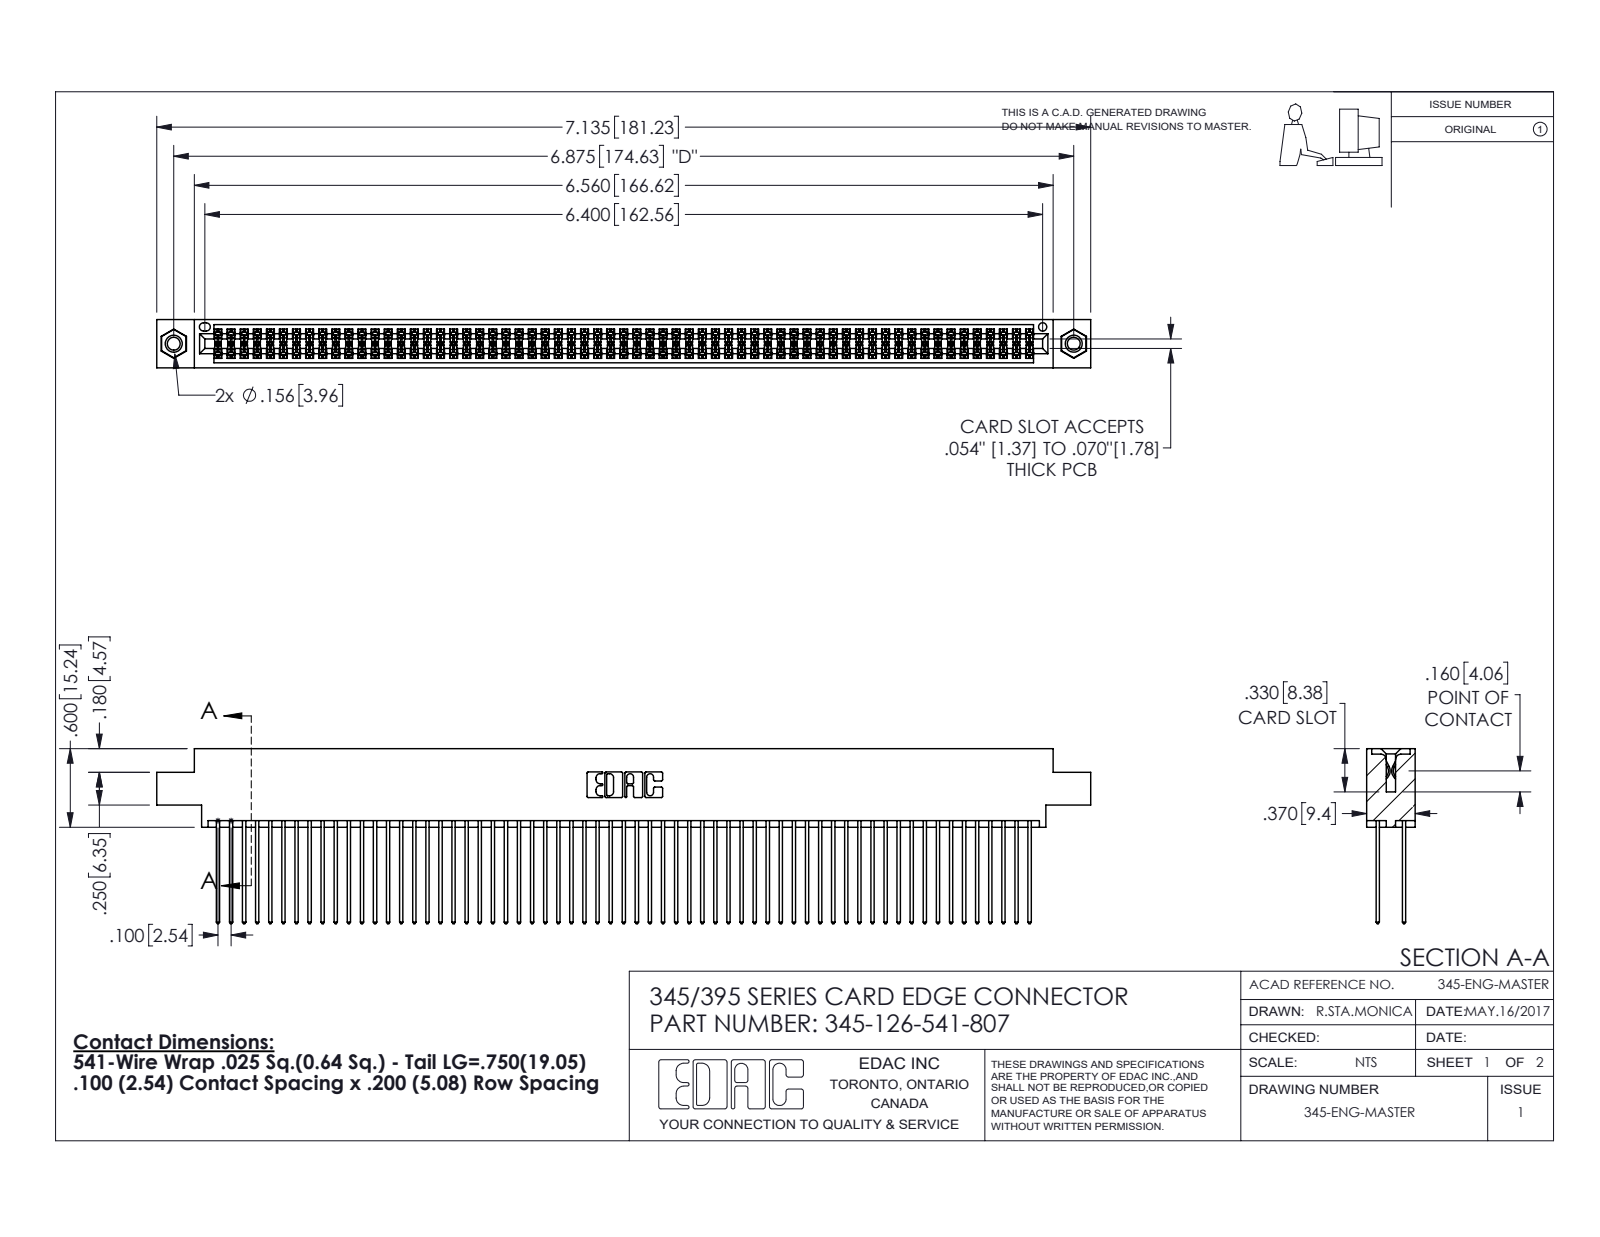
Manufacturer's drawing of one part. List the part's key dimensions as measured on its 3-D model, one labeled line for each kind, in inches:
Part name (STEP PRODUCT): 345-292-001_345-293-141; 345-250-001_345-250-005-103; 345 Part_0.170 Offset - 0.156 Dia-TI; 345-126-541-807
STEP written by: SolidWorks 2016 (CONFIG_CONTROL_DESIGN)
Units: inches
Bodies: 129 solids, 6490 faces (4274 planar, 2200 cylindrical, 16 other)
Overall size (bounding box): 7.135 × 1.337 × 0.37
Volume: 1.123 in³ · Surface area: 48.31 in²
Round holes (diameter × count): ⌀0.098 ×2, ⌀0.125 ×2, ⌀0.156 ×2, ⌀0.064 ×1
Round bosses / shafts (diameter × count): ⌀0.155 ×2
Partial cylindrical surfaces — rounded edges, fillets, slot ends (radius × count): R0.006 ×189, R0.01 ×126, R0.01 ×22, R0.007 ×6, R0.031 ×6, R0.026 ×3, R0.014 ×2, R0.019 ×2
Main face-to-face distances: 0.072, 0.298, 0.2, 0.098, 0.272, 0.025, 0.225, 0.37, 0.175, 0.149
Hole centre spacings: 0.27, 6.639, 6.875
